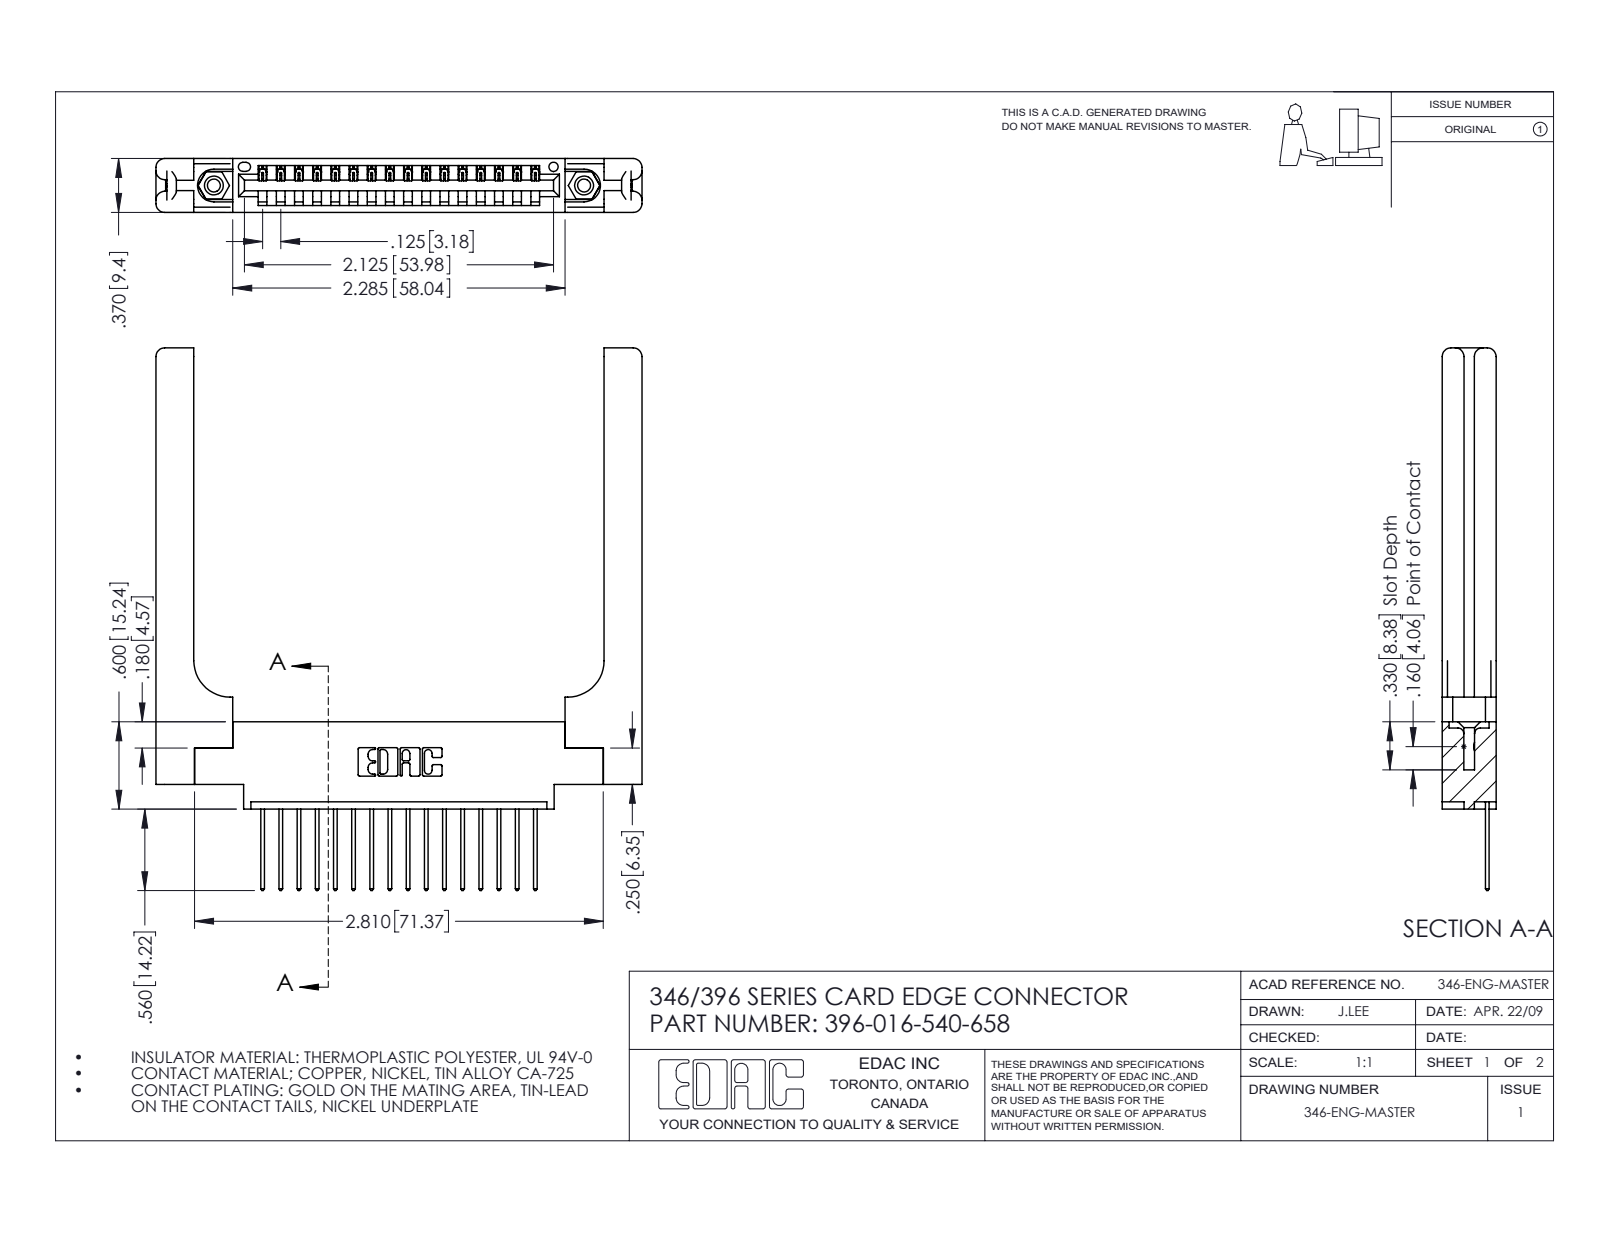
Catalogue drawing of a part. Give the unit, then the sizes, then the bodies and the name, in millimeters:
Units: millimetres
Overall size (bounding box): 94.7 × 84.9 × 9.4
Round holes (diameter × count): ⌀2.3 ×2, ⌀3.2 ×2, ⌀4 ×2, ⌀1.6 ×1
Round bosses / shafts (diameter × count): ⌀3.9 ×2
Partial cylindrical surfaces — rounded edges, fillets, slot ends (radius × count): R0.2 ×32, R0.3 ×32, R0.3 ×22, R1.5 ×16, R0.2 ×6, R0.8 ×6, R0.7 ×3, R0.8 ×2
Main face-to-face distances: 9.4, 1.8, 3.8, 3.8, 1.2, 8.2, 6.4, 2.6, 5.6, 4.4
Hole centre spacings: 6.2, 59.4, 64.6
Volume: 15 300 mm³ · Surface area: 14 970 mm²
Bodies: 21 solids, 1310 faces (868 planar, 382 cylindrical, 60 other)
Part name (STEP PRODUCT): 346-220-058_345-220-058; 396-016-540-658; 346 Part_0.170 Offset - 0.156 Dia-TH; 345-250-001_345-250-001-102 (+1 more)
STEP written by: SolidWorks 2016 (CONFIG_CONTROL_DESIGN)
